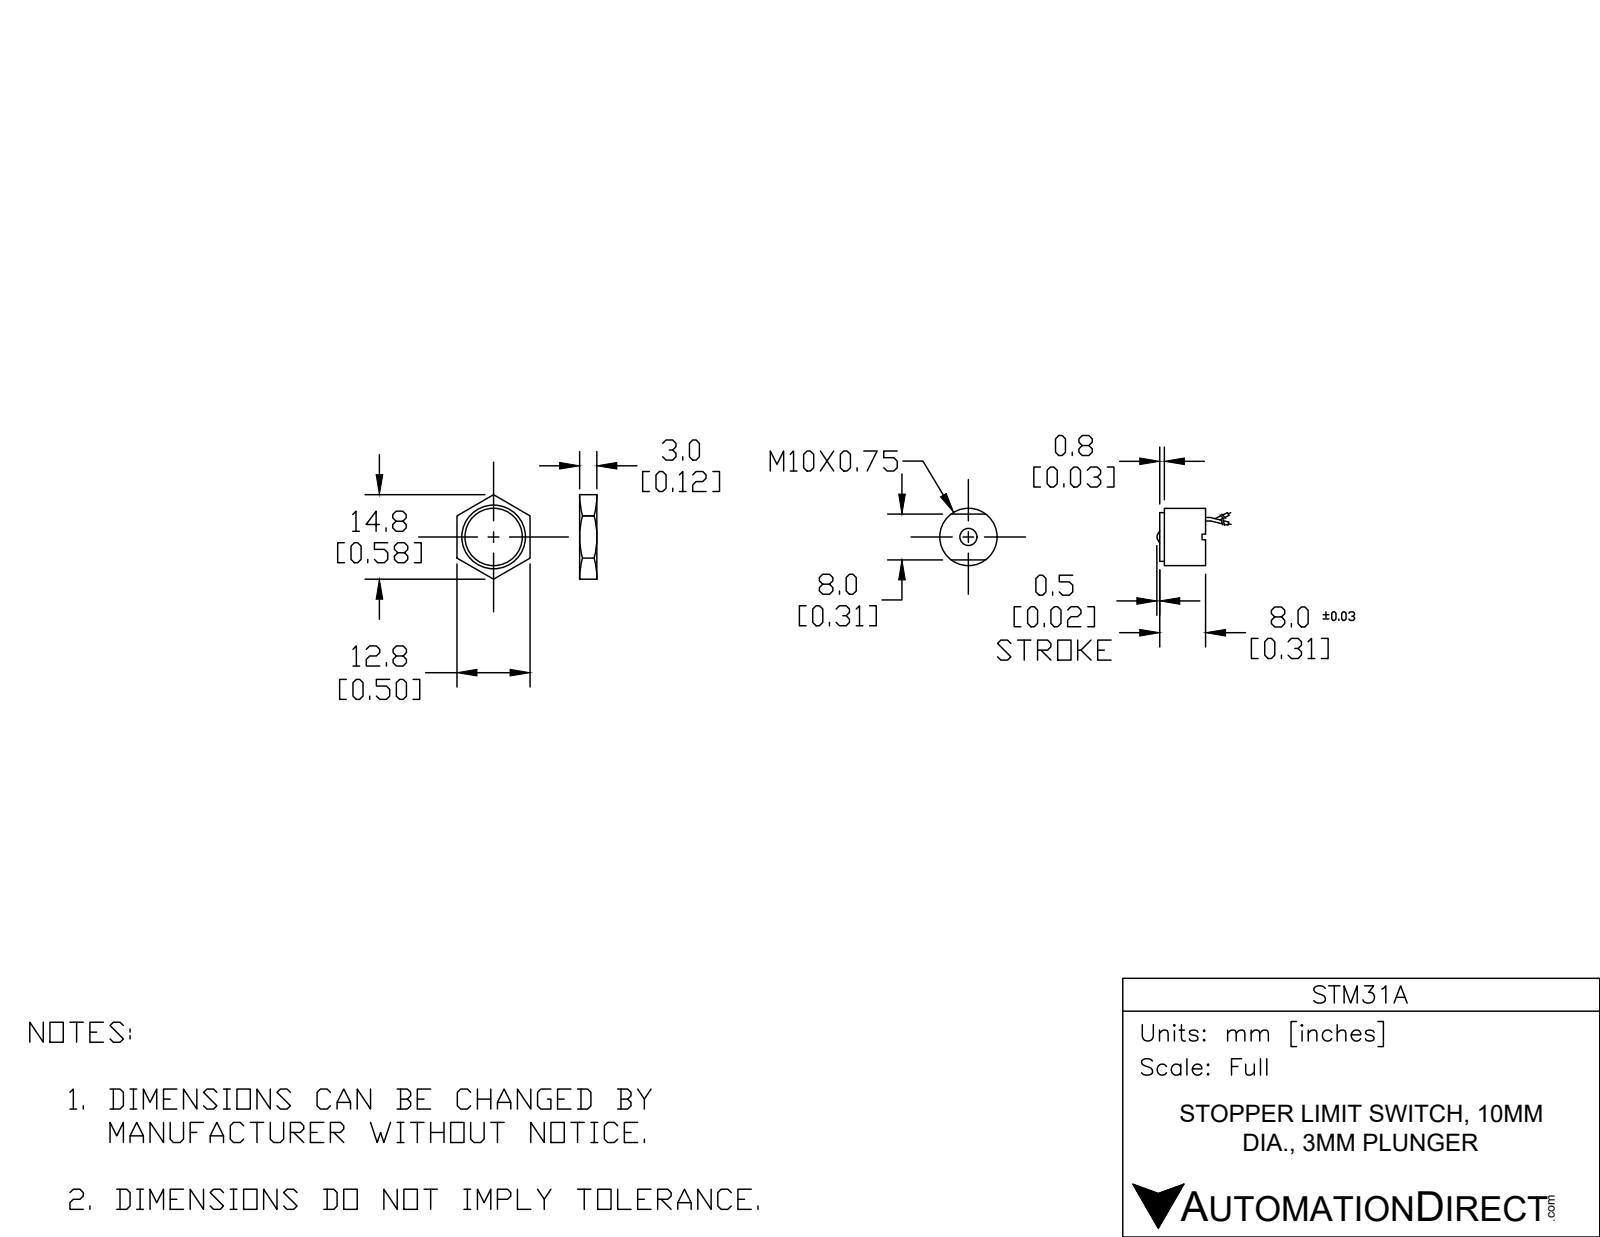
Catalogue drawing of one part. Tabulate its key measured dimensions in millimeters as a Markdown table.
| quantity | value |
| --- | --- |
| part name | STM31A |
| STEP written by | SolidWorks 2016 (CONFIG_CONTROL_DESIGN) |
| units | millimeters |
| bodies | 1 solid, 58 faces (12 planar, 28 cylindrical, 18 other) |
| overall size | 18.5 × 10 × 10 |
| volume | 566 mm³ |
| surface area | 586 mm² |
| round bosses / shafts (diameter × count) | 0.6 × 2, 10 × 1 |
| main face-to-face distances | 8, 7.4, 0.6, 3.5, 4.5, 1, 0.8, 6.6, 7.2, 18 |
